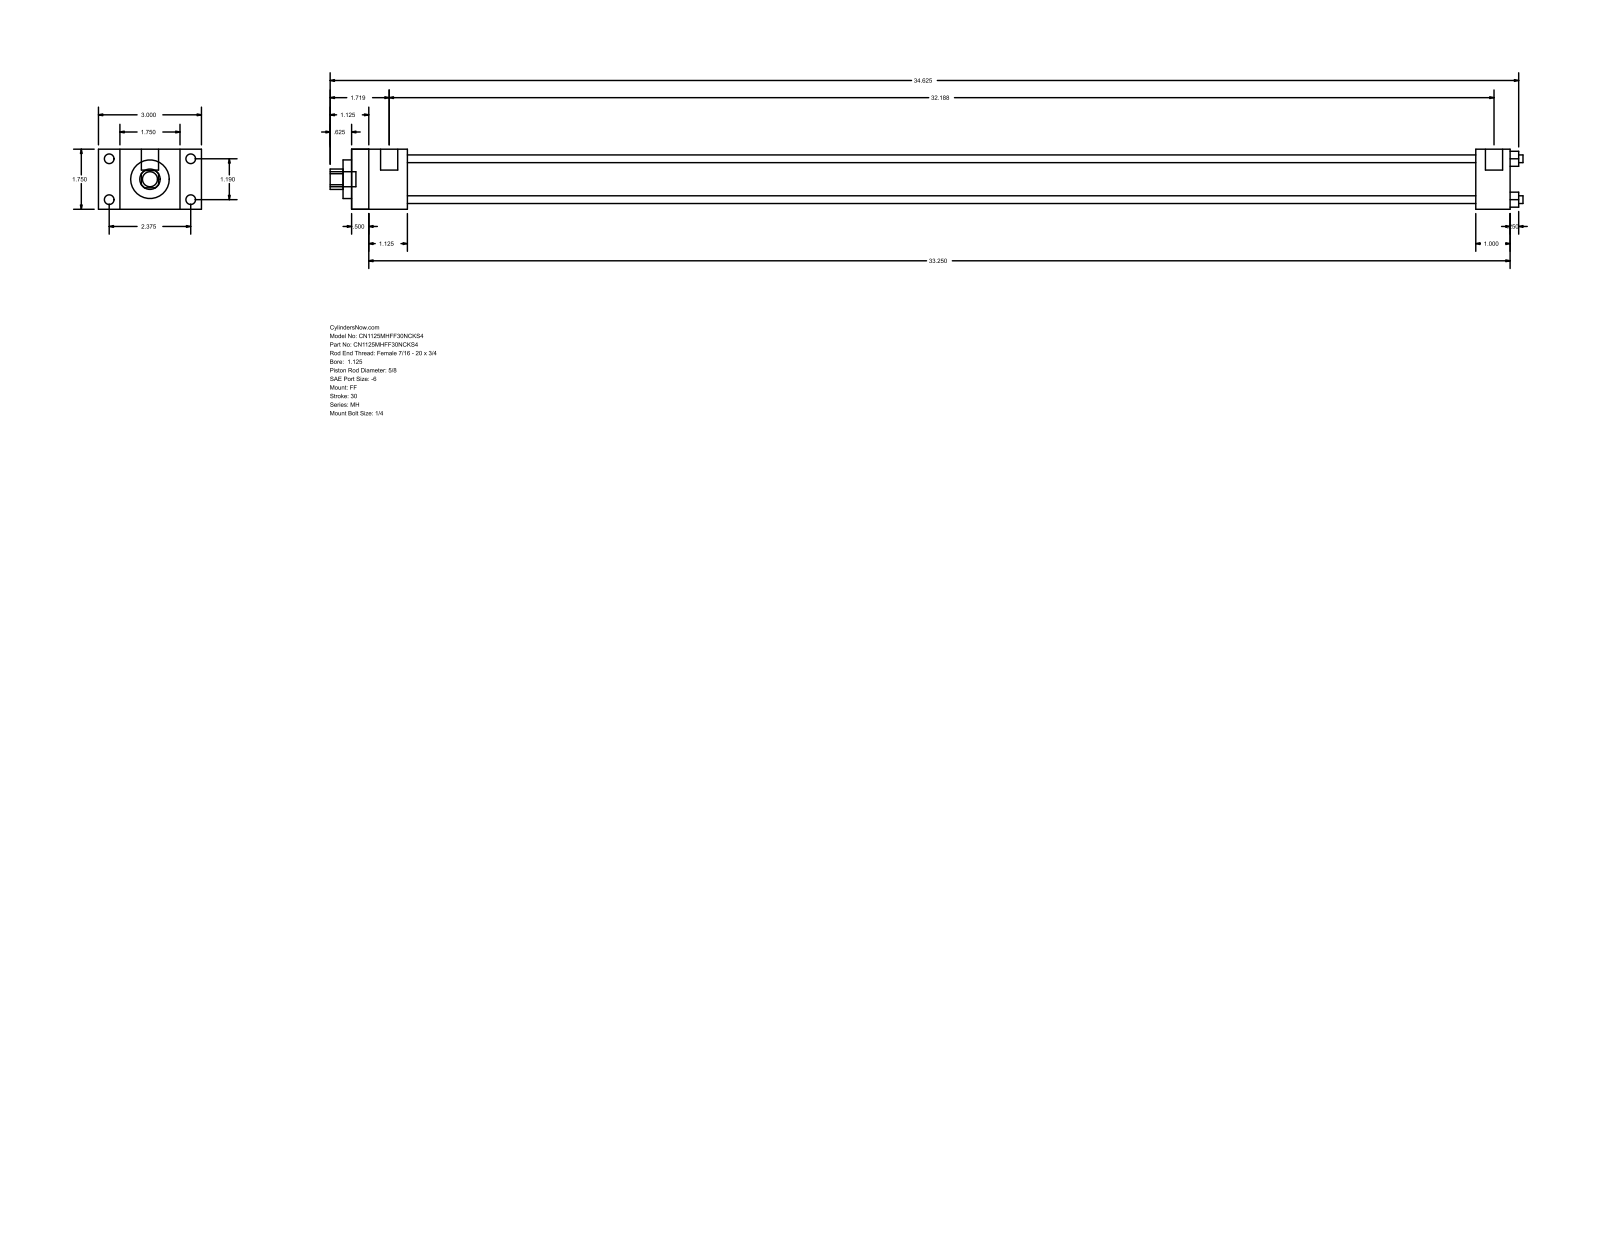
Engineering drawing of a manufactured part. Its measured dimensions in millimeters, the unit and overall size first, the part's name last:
Units: millimetres
Overall size (bounding box): 882.65 × 76.2 × 44.45
Round holes (diameter × count): ⌀5.71 ×4, ⌀15.88 ×1, ⌀28.57 ×1, ⌀34.92 ×1
Round bosses / shafts (diameter × count): ⌀7.14 ×4, ⌀5.56 ×4, ⌀12.7 ×2, ⌀11.11 ×1
Partial cylindrical surfaces — rounded edges, fillets, slot ends (radius × count): R7.54 ×1
Main face-to-face distances: 44.46, 857.24, 15.87, 12.69, 844.55, 60.33, 28.58, 41.27, 831.85, 819.16
Hole centre spacings: 21.37, 30.22, 42.74
Bodies: 0 solids, 92 faces (64 planar, 28 cylindrical, 0 other)
Part name (STEP PRODUCT): MH_FF__0112_0.625
STEP written by: GSSL Pune (CONFIG_CONTROL_DESIGN)
